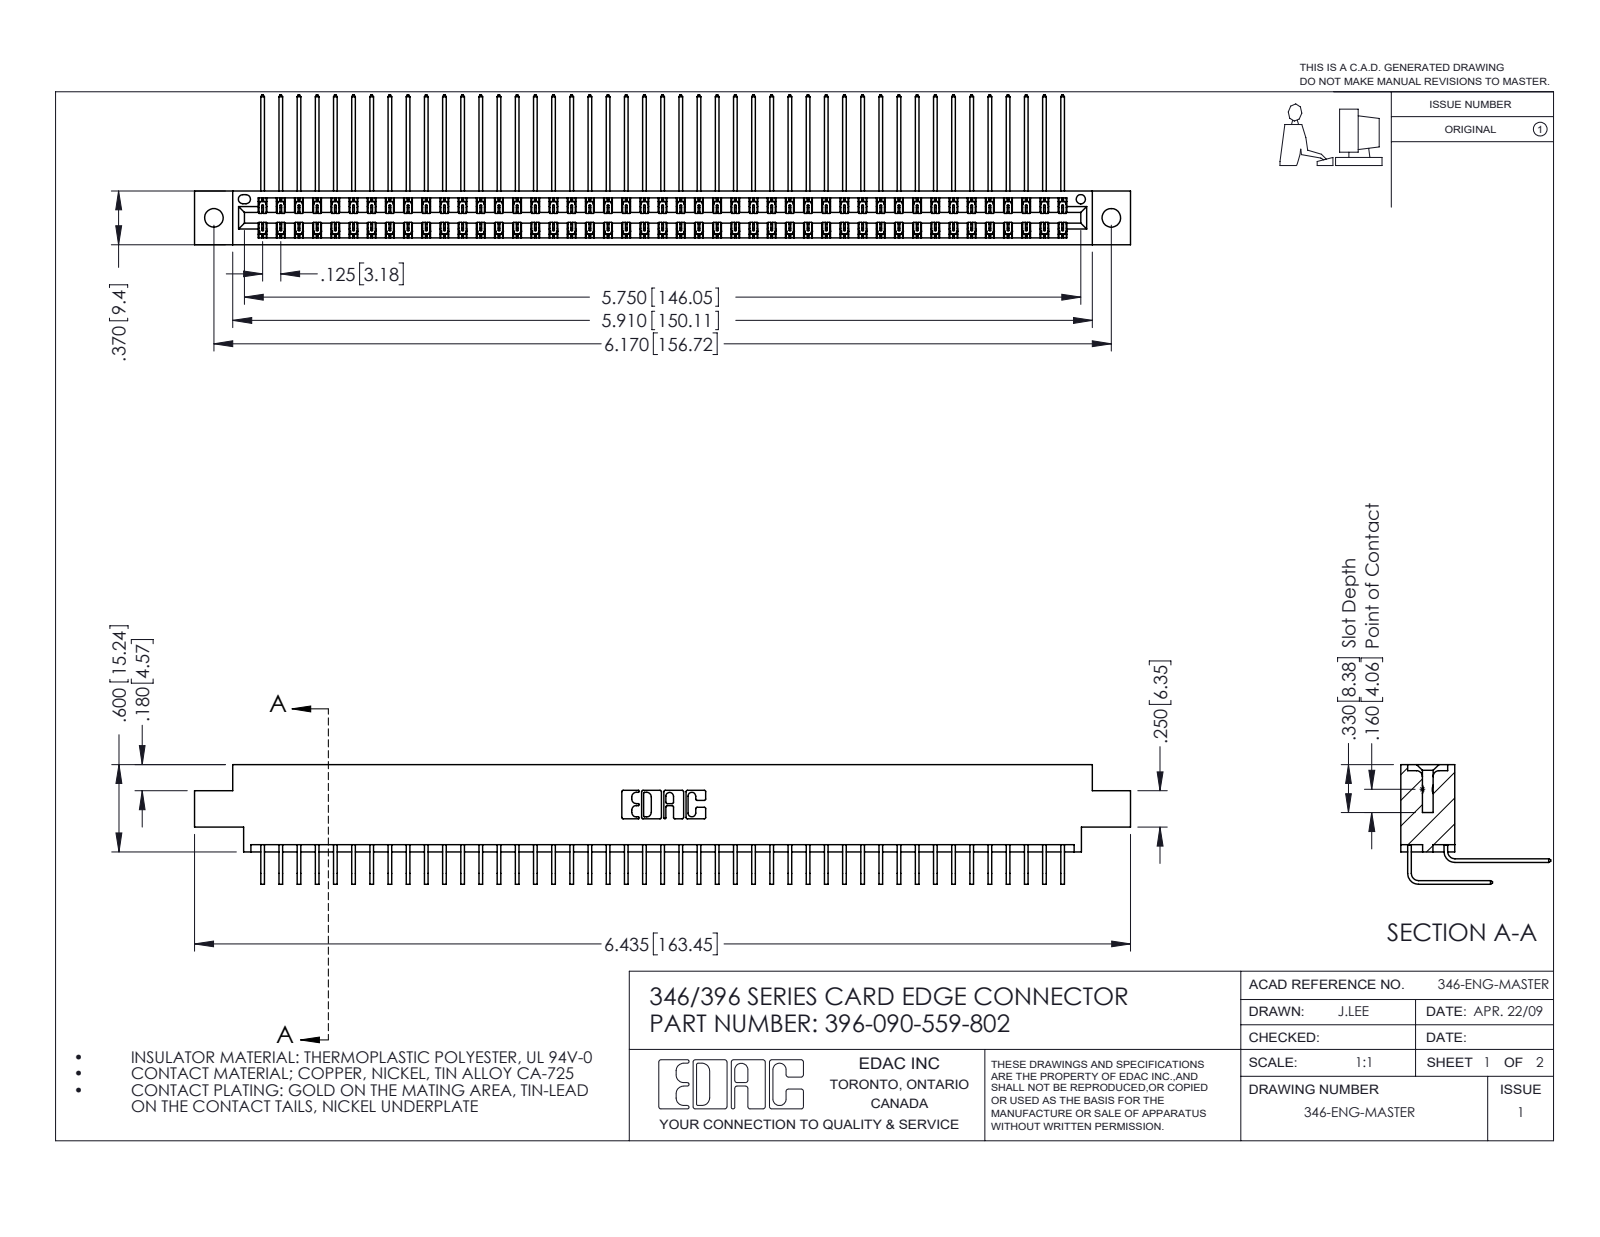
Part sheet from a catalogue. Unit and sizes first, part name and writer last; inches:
Units: inches
Overall size (bounding box): 6.435 × 1.03 × 0.823
Round holes (diameter × count): ⌀0.128 ×2, ⌀0.064 ×1
Partial cylindrical surfaces — rounded edges, fillets, slot ends (radius × count): R0.006 ×135, R0.01 ×22, R0.007 ×6, R0.031 ×6, R0.026 ×3, R0.014 ×2, R0.022 ×2, R0.024 ×2
Main face-to-face distances: 0.048, 0.322, 0.025, 0.37, 0.25, 0.072, 0.298, 0.275, 0.148, 0.222
Hole centre spacings: 0.246, 5.961, 6.17
Volume: 0.994 in³ · Surface area: 38.5 in²
Bodies: 91 solids, 4986 faces (3410 planar, 1576 cylindrical, 0 other)
Part name (STEP PRODUCT): 345-292-001_559 Tail - 2; 396-090-559-802; 345-292-001_558 559 Tail - 1; 346 Part_0.170 Offset - 0.128 Dia
STEP written by: SolidWorks 2016 (CONFIG_CONTROL_DESIGN)
